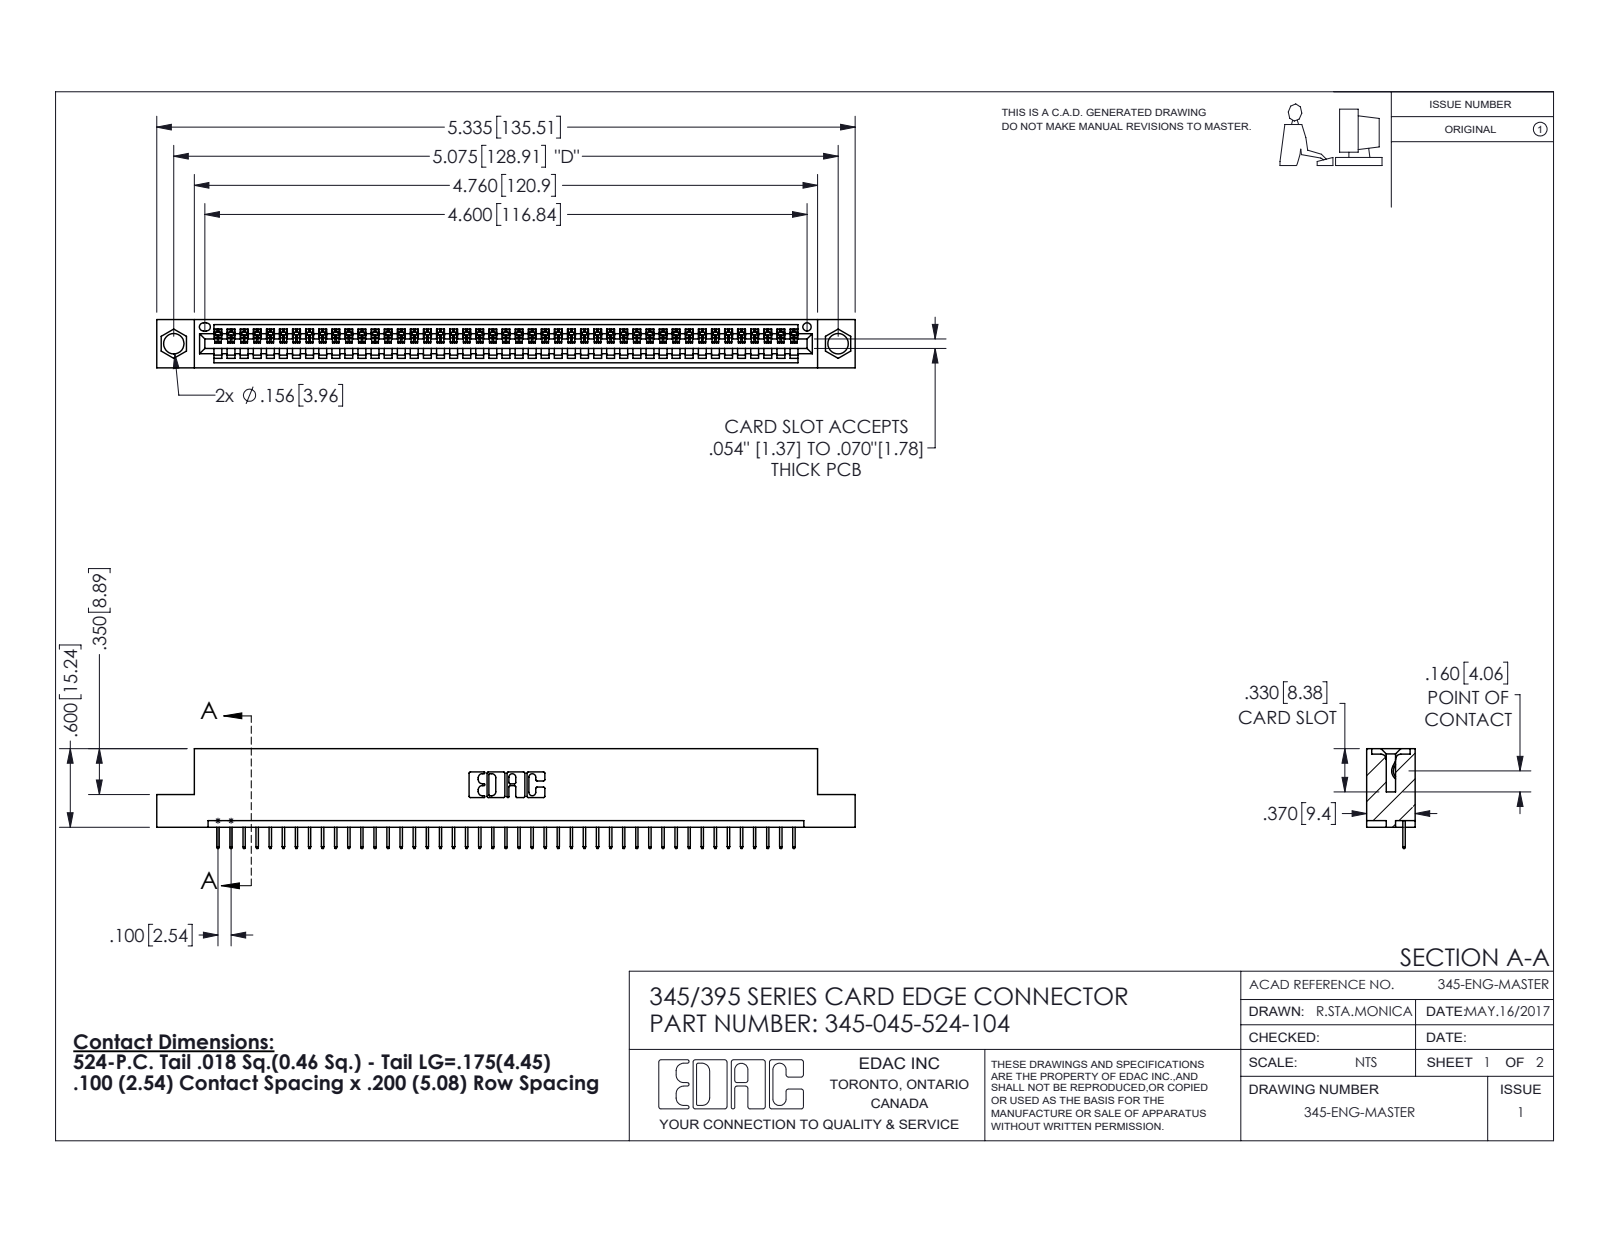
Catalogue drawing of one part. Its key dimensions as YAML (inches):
part_name: "345 Part_Flush Mounting Lugs - 0.156 Dia-TH; 345-292-001_345-293-124; 345-045-524-104"
step_written_by: "SolidWorks 2016 (CONFIG_CONTROL_DESIGN)"
units: inches
bodies: {solids: 46, faces: 2916, planar: 2150, cylindrical: 766, other: 0}
overall_size: [5.335, 0.762, 0.37]
volume: 0.771
surface_area: 24.9
round_holes:
  - {diameter: 0.156, count: 2}
  - {diameter: 0.064, count: 1}
partial_cylinders:
  - {radius: 0.006, count: 90}
  - {radius: 0.01, count: 22}
  - {radius: 0.007, count: 6}
  - {radius: 0.031, count: 6}
  - {radius: 0.026, count: 3}
  - {radius: 0.031, count: 2}
  - {radius: 0.04, count: 2}
  - {radius: 0.014, count: 1}
face_to_face_distances: [0.298, 0.072, 0.37, 0.2, 0.098, 0.272, 0.025, 0.225, 0.072, 0.149]
hole_center_spacings: [0.27, 4.839, 5.075]
